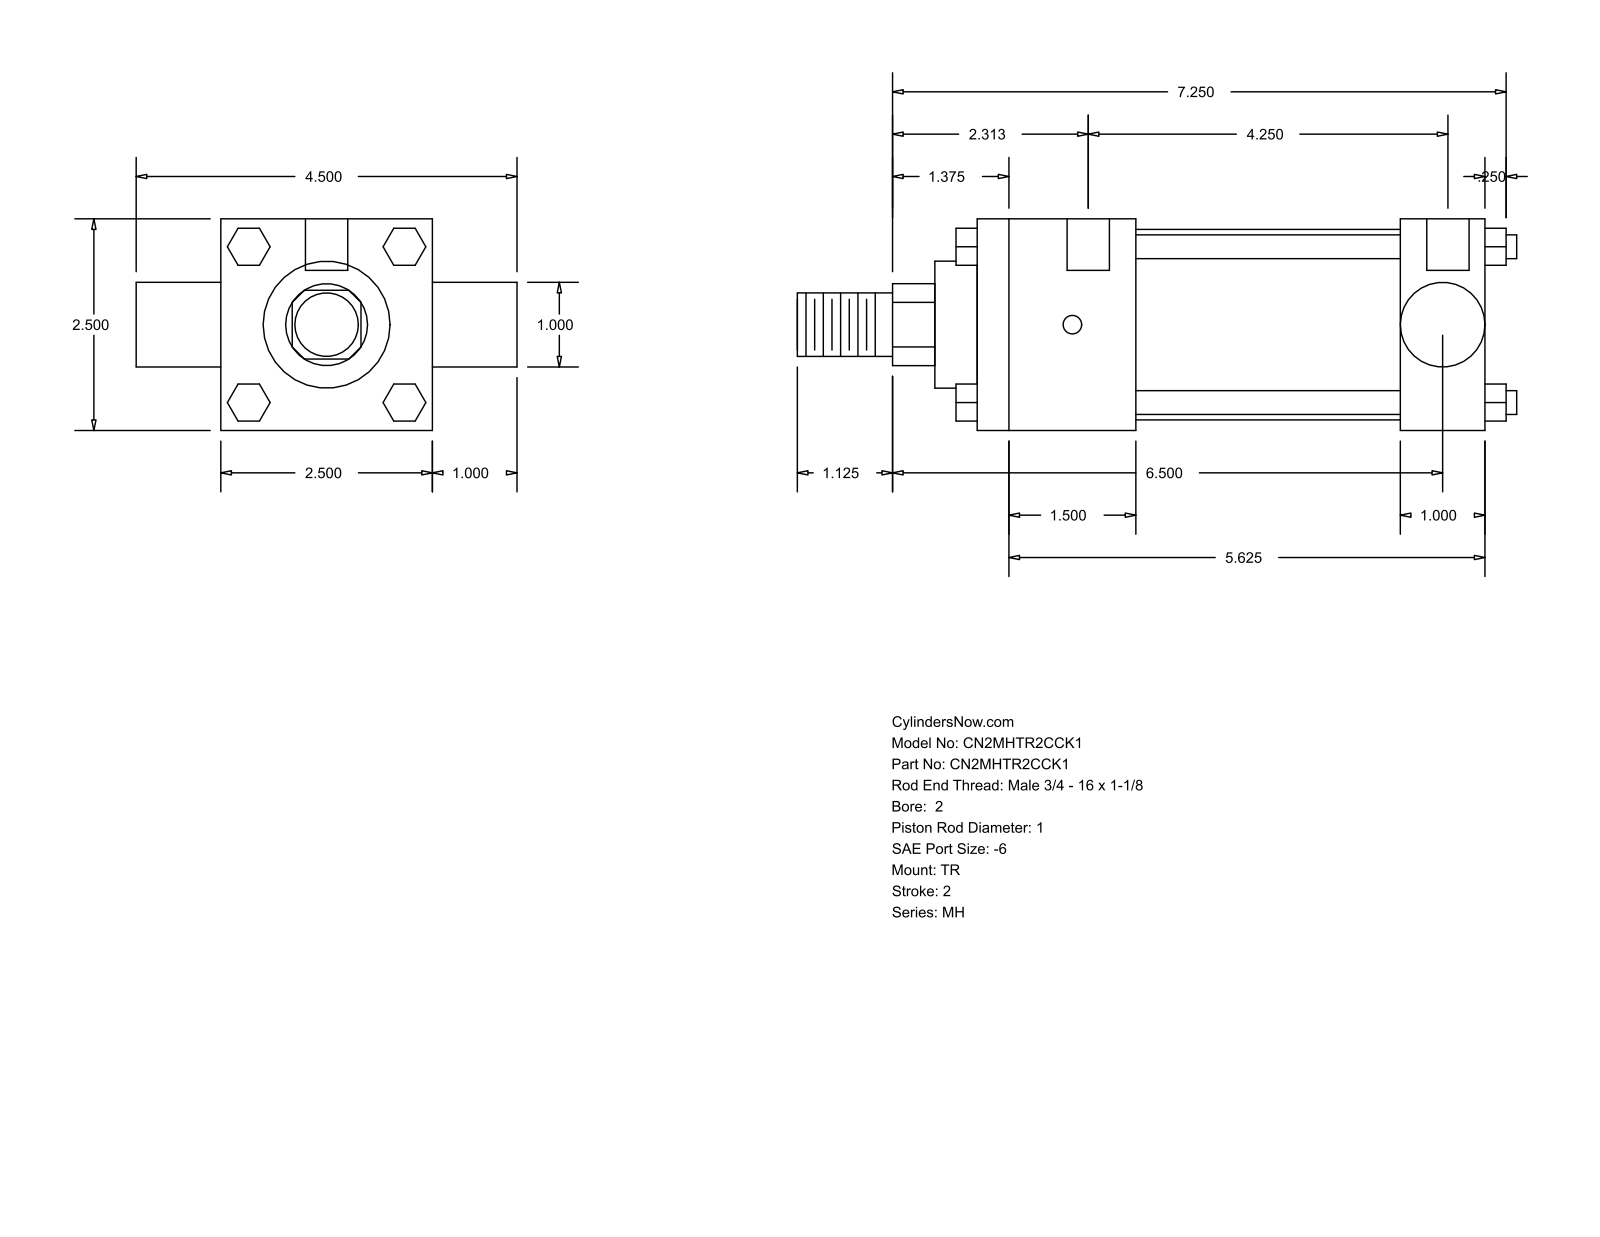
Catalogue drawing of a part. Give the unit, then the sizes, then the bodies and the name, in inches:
Units: inches
Overall size (bounding box): 8.5 × 4.5 × 2.5
Round holes (diameter × count): ⌀0.219 ×3, ⌀0.5 ×2
Round bosses / shafts (diameter × count): ⌀0.281 ×4, ⌀2.25 ×1, ⌀1.5 ×1, ⌀1 ×1, ⌀0.998 ×1, ⌀0.75 ×1
Partial cylindrical surfaces — rounded edges, fillets, slot ends (radius × count): R0.484 ×1
Main face-to-face distances: 2.5, 6, 1, 1.875, 5, 3.125, 4.125, 3.5, 6.5, 0.25
Hole centre spacings: 0.125, 0.187, 4.25, 4.375, 4.437, 4.562
Bodies: 0 solids, 120 faces (92 planar, 28 cylindrical, 0 other)
Part name (STEP PRODUCT): MH_TR__0200_1
STEP written by: GSSL Pune (CONFIG_CONTROL_DESIGN)
